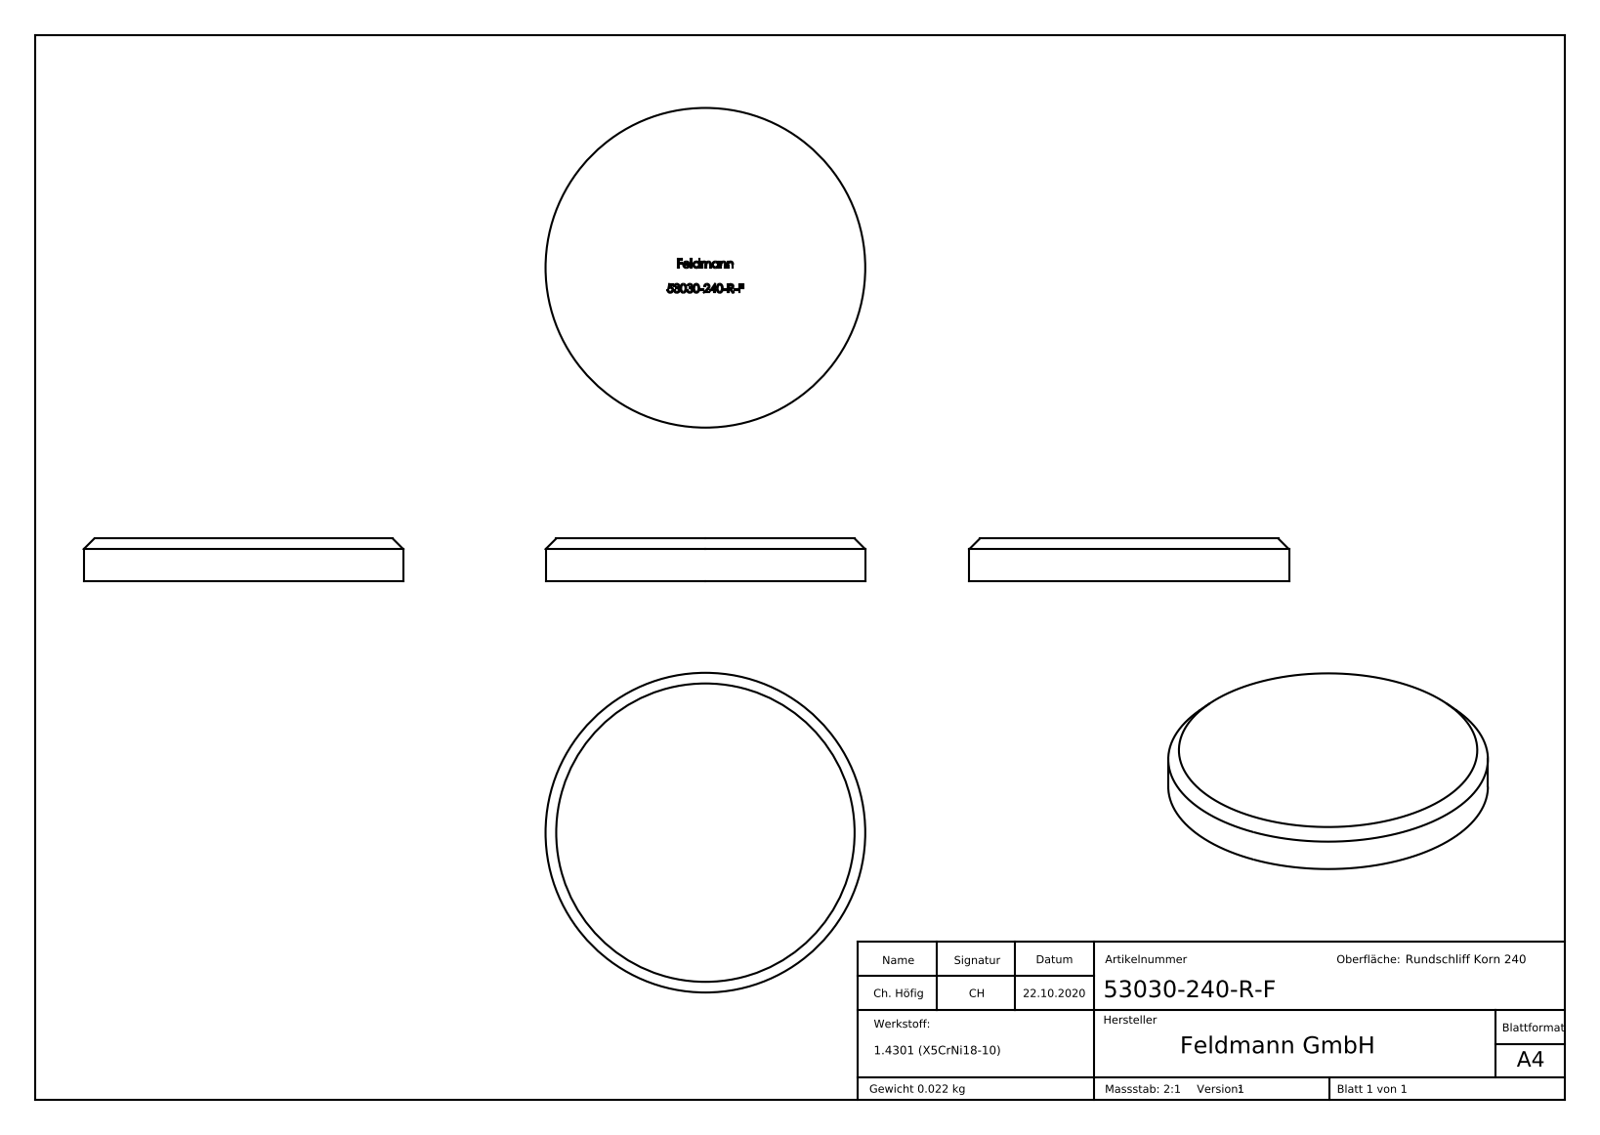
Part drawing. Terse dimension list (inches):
name: 53030-240-R-F
written by: SolidWorks 2018 (CONFIG_CONTROL_DESIGN)
unit: in
bodies: 1 solid, 275 faces (149 planar, 2 cylindrical, 124 other)
size: 1.181 × 1.181 × 0.157
volume: 0.17 in³; area: 2.699 in²
bosses: 1× ⌀1.181
face distances: 0.157, 0.154, 0.091, 0.048, 0.137, 0.031, 0.07, 0.087, 0.088, 0.033
